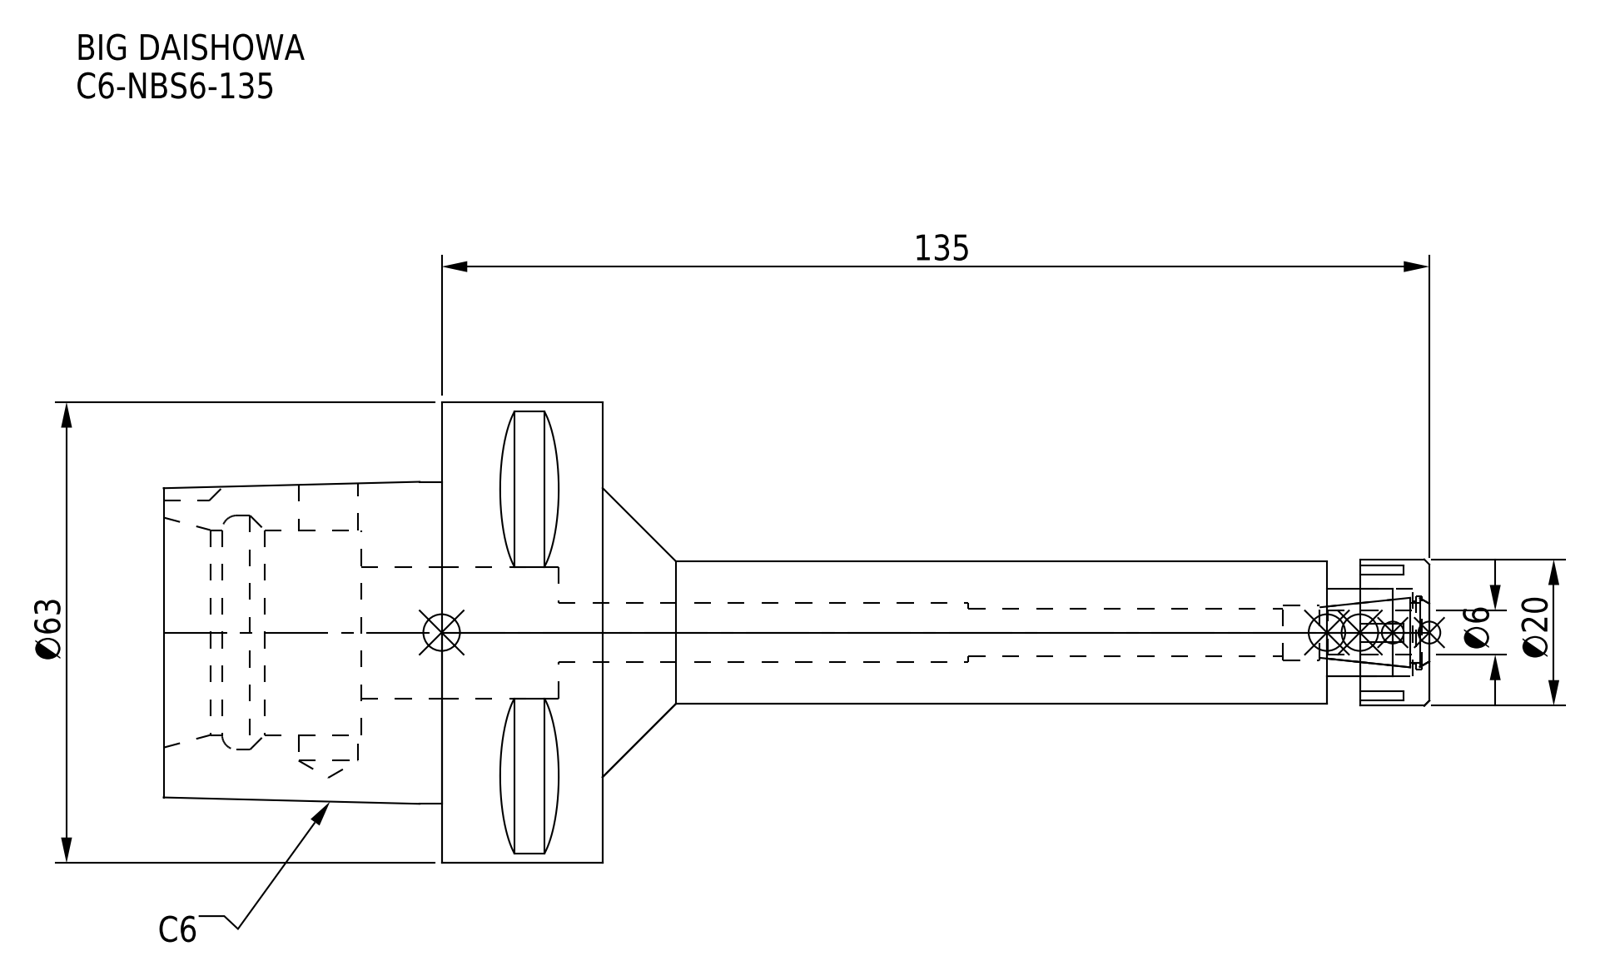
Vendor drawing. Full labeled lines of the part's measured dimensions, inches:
Part name (STEP PRODUCT): C6-NBS6-135.stp; C6-NBS6-135-FreeParts; DXF_TEMP_ASSY_ASM_4_ASM.stp; C6-NBS6-135 (+3 more)
STEP written by: SolidWorks 2019 (CONFIG_CONTROL_DESIGN)
Units: inches
Bodies: 2 solids, 112 faces (61 planar, 33 cylindrical, 18 other)
Overall size (bounding box): 6.811 × 2.48 × 2.48
Volume: 7.825 in³ · Surface area: 47.2 in²
Round holes (diameter × count): ⌀0.252 ×1, ⌀0.295 ×1, ⌀0.315 ×1, ⌀0.319 ×1, ⌀0.335 ×1, ⌀0.394 ×1, ⌀0.472 ×1, ⌀0.709 ×1, ⌀1.102 ×1, ⌀1.26 ×1
Round bosses / shafts (diameter × count): ⌀2.48 ×1, ⌀0.787 ×1, ⌀0.768 ×1
Partial cylindrical surfaces — rounded edges, fillets, slot ends (radius × count): R0.197 ×1
Main face-to-face distances: 0.866, 1.063, 2.362, 1.496, 1.299, 0.433, 0.98, 2.181, 0.236, 0.177
